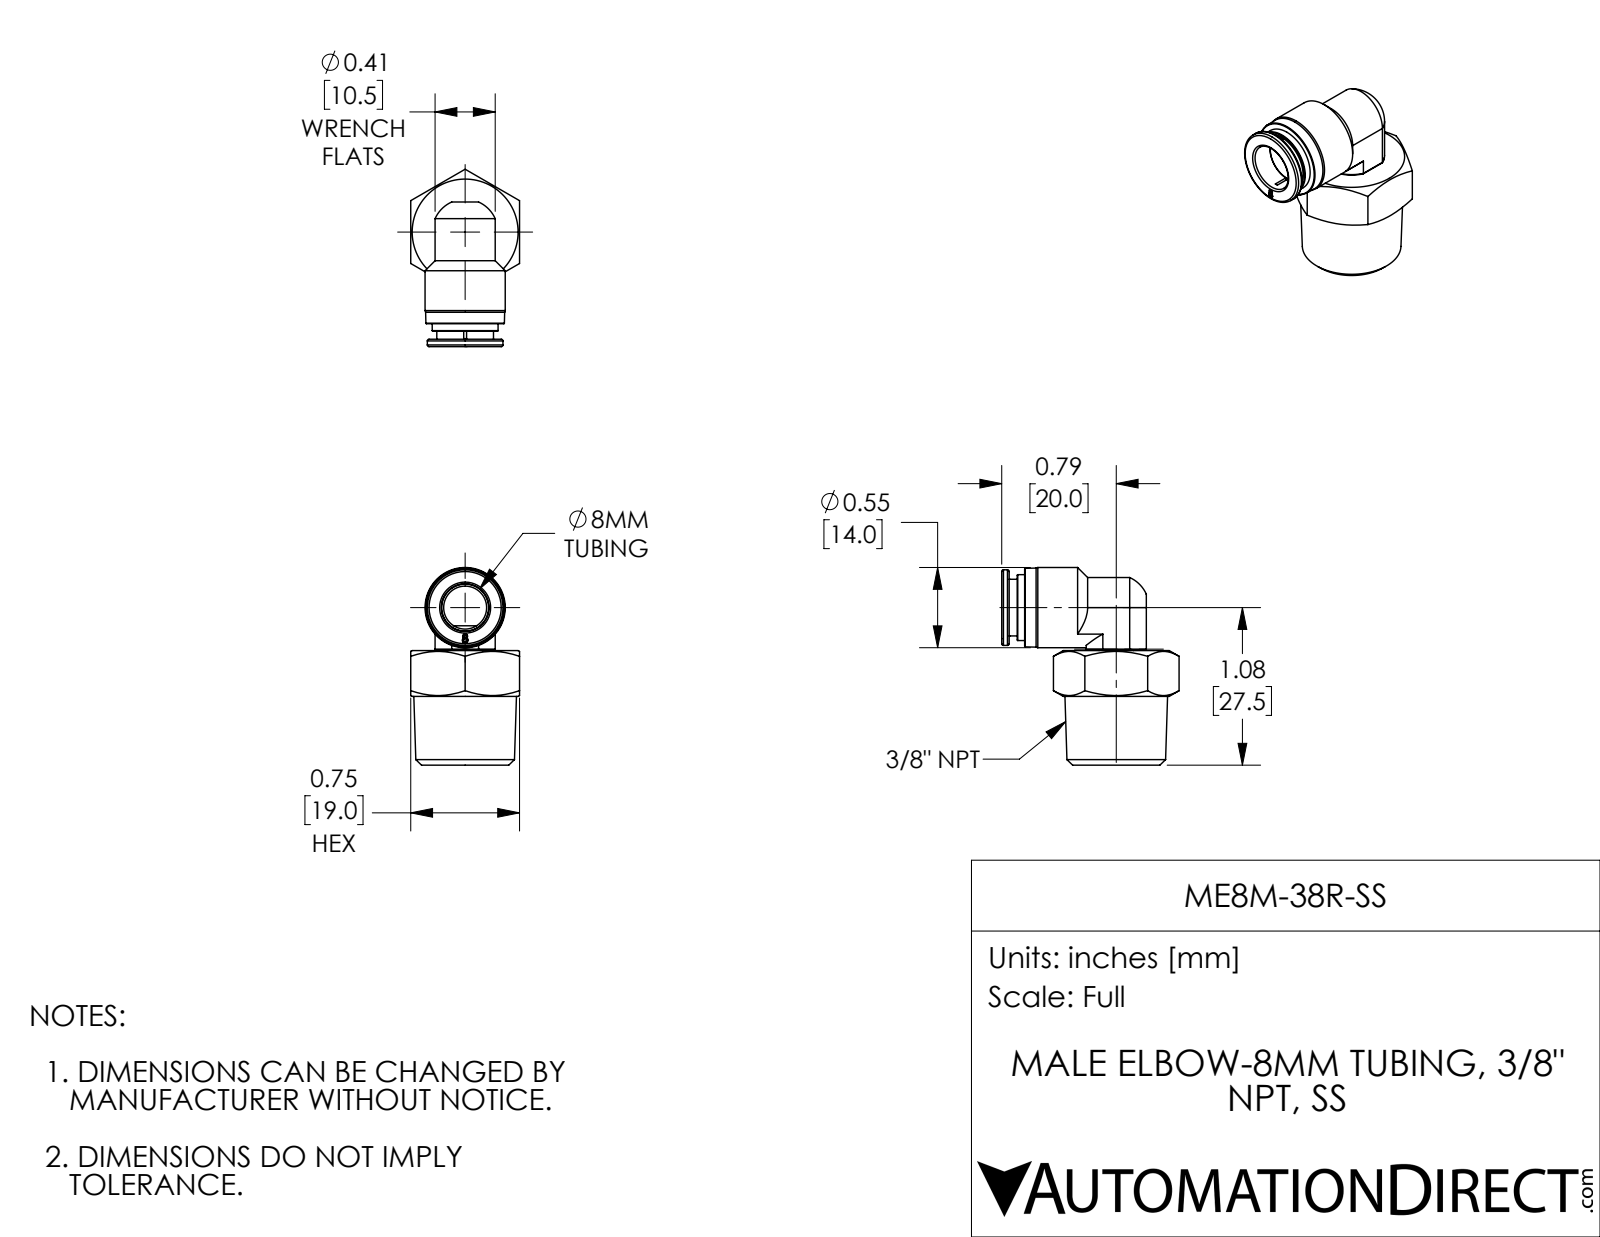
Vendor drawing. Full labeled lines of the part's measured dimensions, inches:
Part name (STEP PRODUCT): ME8M-38R-SS
STEP written by: SolidWorks 2017 (AUTOMOTIVE_DESIGN)
Units: inches
Bodies: 2 solids, 118 faces (31 planar, 34 cylindrical, 53 other)
Overall size (bounding box): 1.358 × 1.219 × 0.748
Volume: 0.432 in³ · Surface area: 6.606 in²
Round holes (diameter × count): ⌀0.157 ×1, ⌀0.238 ×1, ⌀0.295 ×1, ⌀0.323 ×1, ⌀0.327 ×1, ⌀0.394 ×1
Round bosses / shafts (diameter × count): ⌀0.551 ×1, ⌀0.52 ×1, ⌀0.453 ×1, ⌀0.39 ×1, ⌀0.236 ×1
Partial cylindrical surfaces — rounded edges, fillets, slot ends (radius × count): R0.008 ×4, R0.207 ×1, R0.226 ×1
Main face-to-face distances: 0.748, 0.787, 0.581, 0.167, 0.789, 0.051, 0.106, 0.413, 0.157, 0.837
